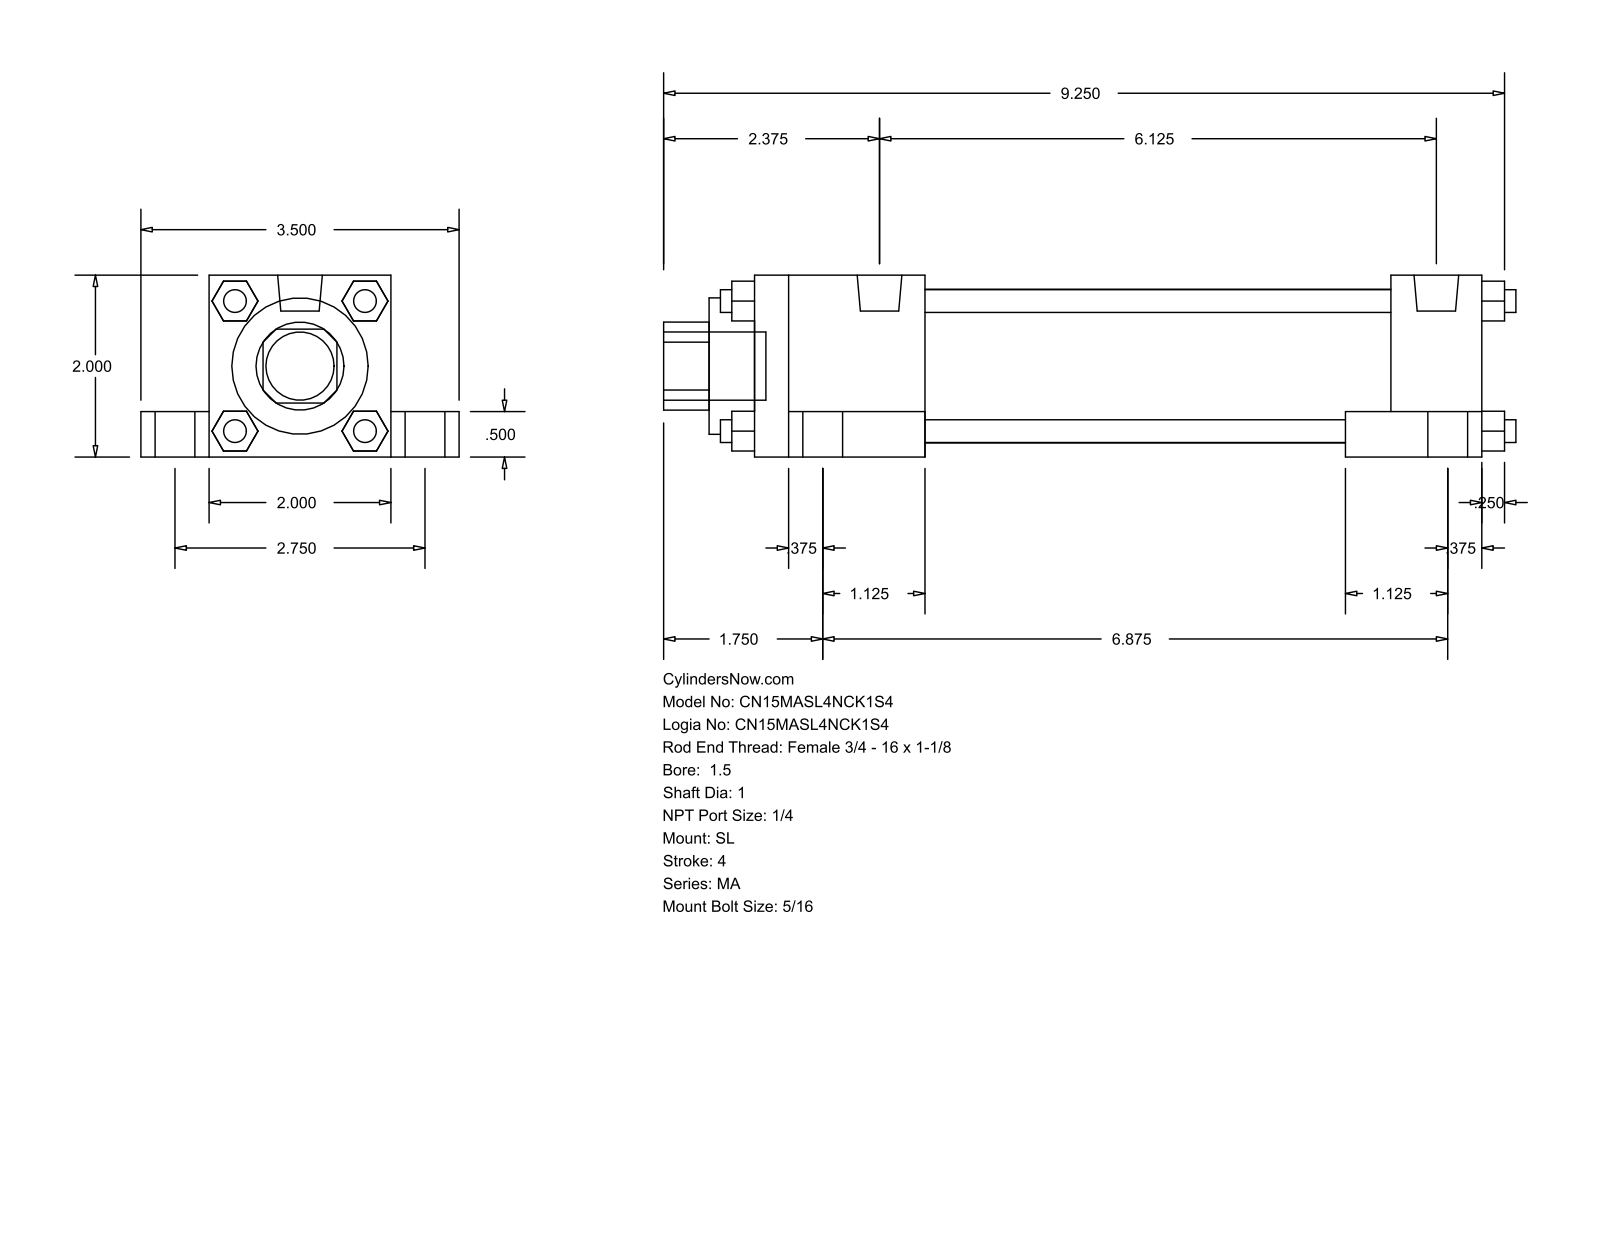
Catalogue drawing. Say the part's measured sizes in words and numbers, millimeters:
The part is named "MA_SL__0150_1". Its 3-D file was written by "GSSL Pune (CONFIG_CONTROL_DESIGN)". It is 0 solids with 148 faces: 112 planar, 36 cylindrical and 0 other. Overall it measures 238.12 by 88.9 by 50.8 millimeters. Round holes: 1 of diameter 25.4, 1 of diameter 38.1, 1 of diameter 42.93. Round bosses or shafts: 4 of diameter 17.46, 4 of diameter 11.11, 4 of diameter 7.94, 4 of diameter 6.35, 2 of diameter 12.49, 1 of diameter 19.05. Partial cylindrical surfaces (rounded edges, fillets, slot ends): 1 of radius 12.29. The main face-to-face distances are 50.8, 12.7, 19.05, 9.52, 69.85, 38.1, 6.35, 203.2, 25.4, 177.8.
